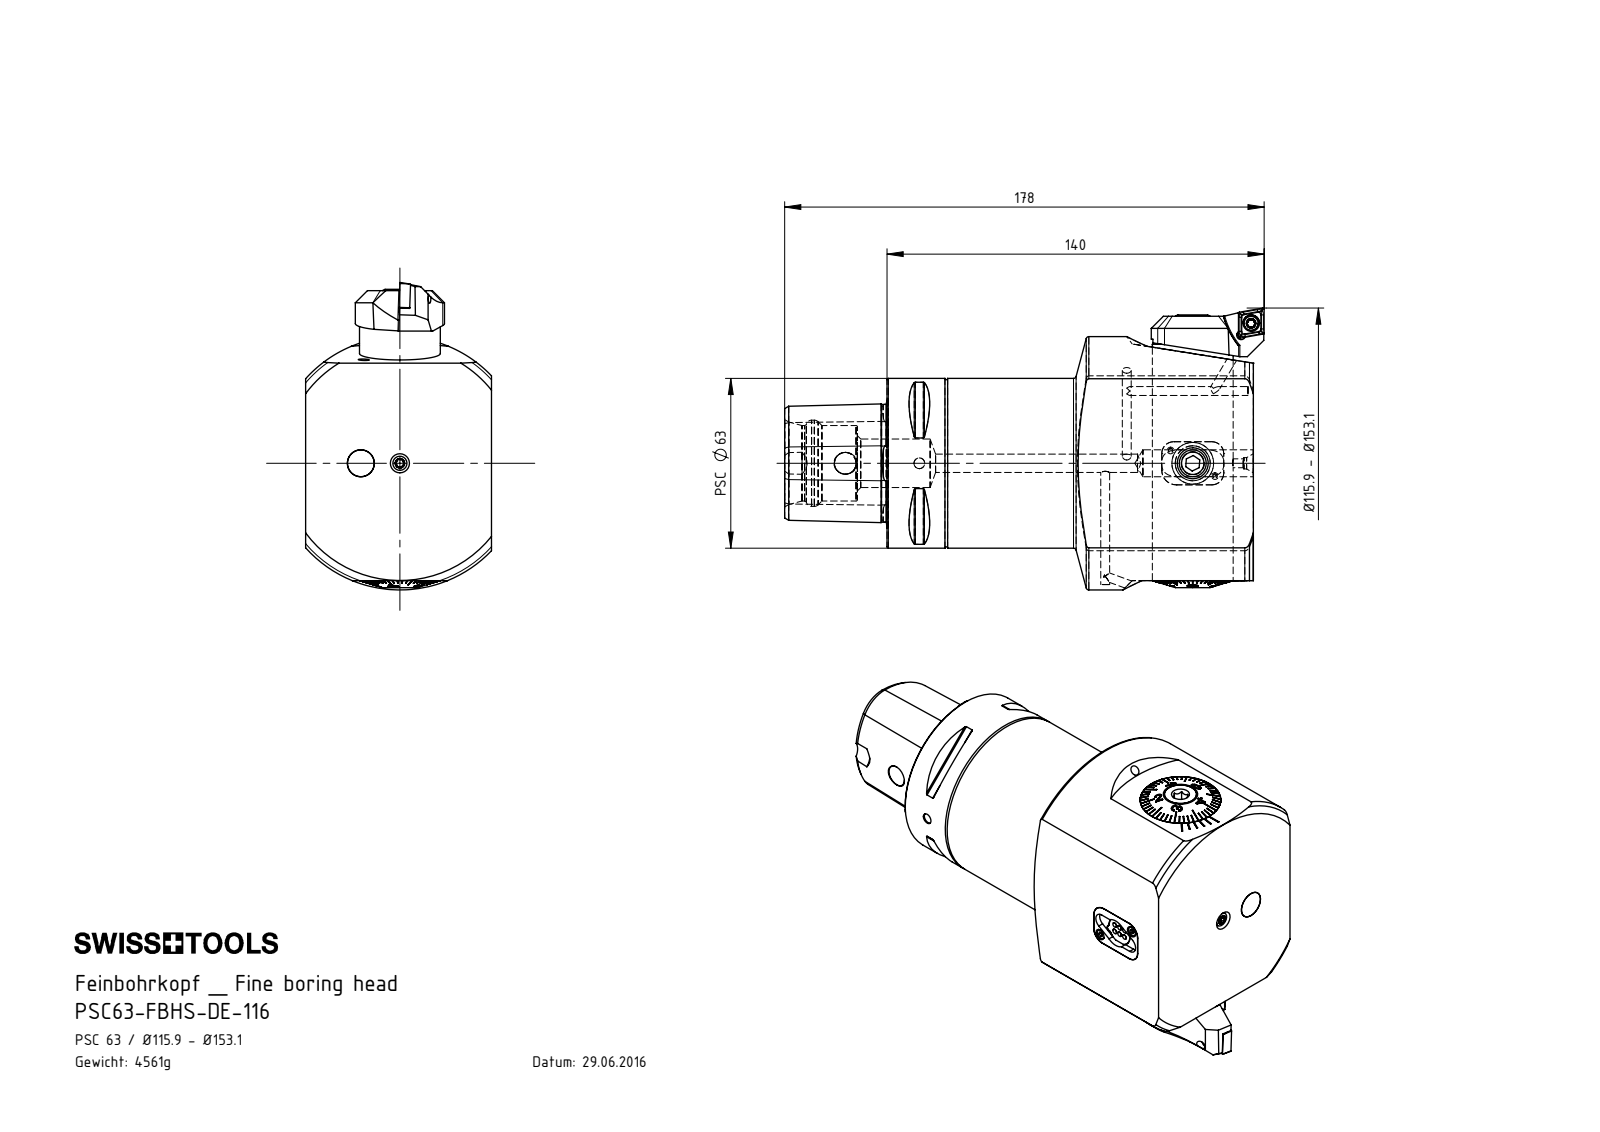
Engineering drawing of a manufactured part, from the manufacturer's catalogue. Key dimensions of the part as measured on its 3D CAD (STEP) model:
Part name (STEP PRODUCT): F55-BG1.012.012_A; Fxx-MAB.xxx.xxx_A_F94; A55-BG3.011.033_A_gekrzt; A55-BG2.012.006_B (+8 more)
STEP written by: SolidWorks 2017 (AUTOMOTIVE_DESIGN)
Units: millimetres
Bodies: 20 solids, 799 faces (413 planar, 147 cylindrical, 239 other)
Overall size (bounding box): 174 × 102.05 × 69
Volume: 605 099 mm³ · Surface area: 88 961 mm²
Round holes (diameter × count): ⌀3.3 ×7, ⌀4.2 ×3, ⌀1.6 ×2, ⌀2.2 ×2, ⌀8.5 ×2, ⌀13 ×2, ⌀4 ×1, ⌀5 ×1, ⌀6.8 ×1, ⌀8 ×1, ⌀8.1 ×1, ⌀9.5 ×1
Round bosses / shafts (diameter × count): ⌀1.9 ×6, ⌀10 ×2, ⌀3.8 ×2, ⌀2 ×2, ⌀63 ×1, ⌀30 ×1, ⌀29.98 ×1, ⌀29.9 ×1
Partial cylindrical surfaces — rounded edges, fillets, slot ends (radius × count): R0.5 ×10, R0.34 ×6, R0.59 ×6, R1.1 ×6, R1.2 ×6, R4.5 ×4, R3.2 ×3, R4.4 ×3
Main face-to-face distances: 69, 136, 6.5, 5.3, 1.2, 2.8, 2.5, 3.7, 81.6, 84.4
Hole centre spacings: 9.52, 14.5, 19.04, 27.5, 27.98, 32.5, 35, 93.37
